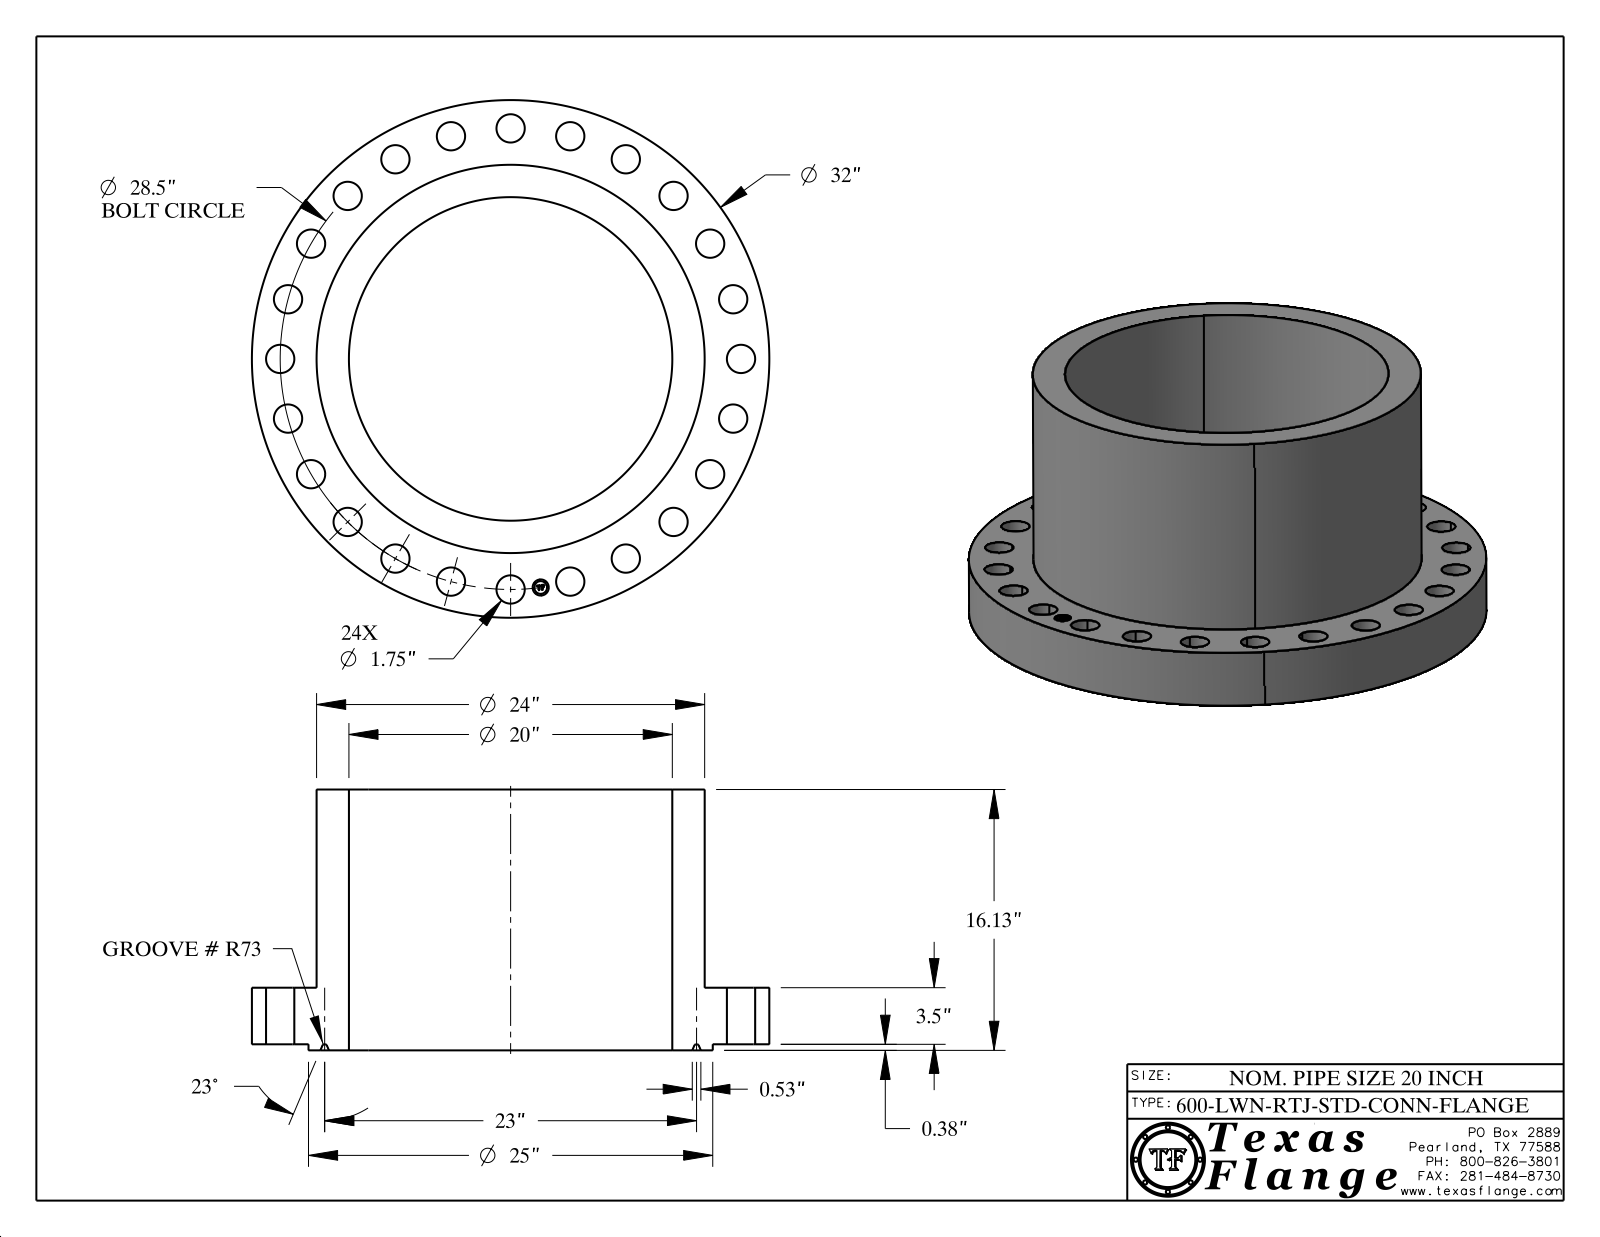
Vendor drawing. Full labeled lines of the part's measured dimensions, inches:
Part name (STEP PRODUCT): 20-600-LWN-RTJ-STD-CONN-FLANGE
STEP written by: CATIA V5 STEP AP214 (AUTOMOTIVE_DESIGN)
Units: inches
Bodies: 1 solid, 455 faces (371 planar, 76 cylindrical, 8 other)
Overall size (bounding box): 32 × 32 × 16.125
Volume: 3 263 in³ · Surface area: 3 679 in²
Round holes (diameter × count): ⌀1.75 ×24, ⌀1 ×1, ⌀20 ×1
Round bosses / shafts (diameter × count): ⌀0.061 ×8, ⌀32 ×1, ⌀25 ×1, ⌀24 ×1, ⌀0.788 ×1
Main face-to-face distances: 3.5, 0.375, 3.875, 16.125, 15.75, 12.25, 3.87, 3.495, 12.255, 0.298
Hole centre spacings: 14.25, 3.72, 7.376, 24.682, 26.331, 27.529, 20.153, 10.907
